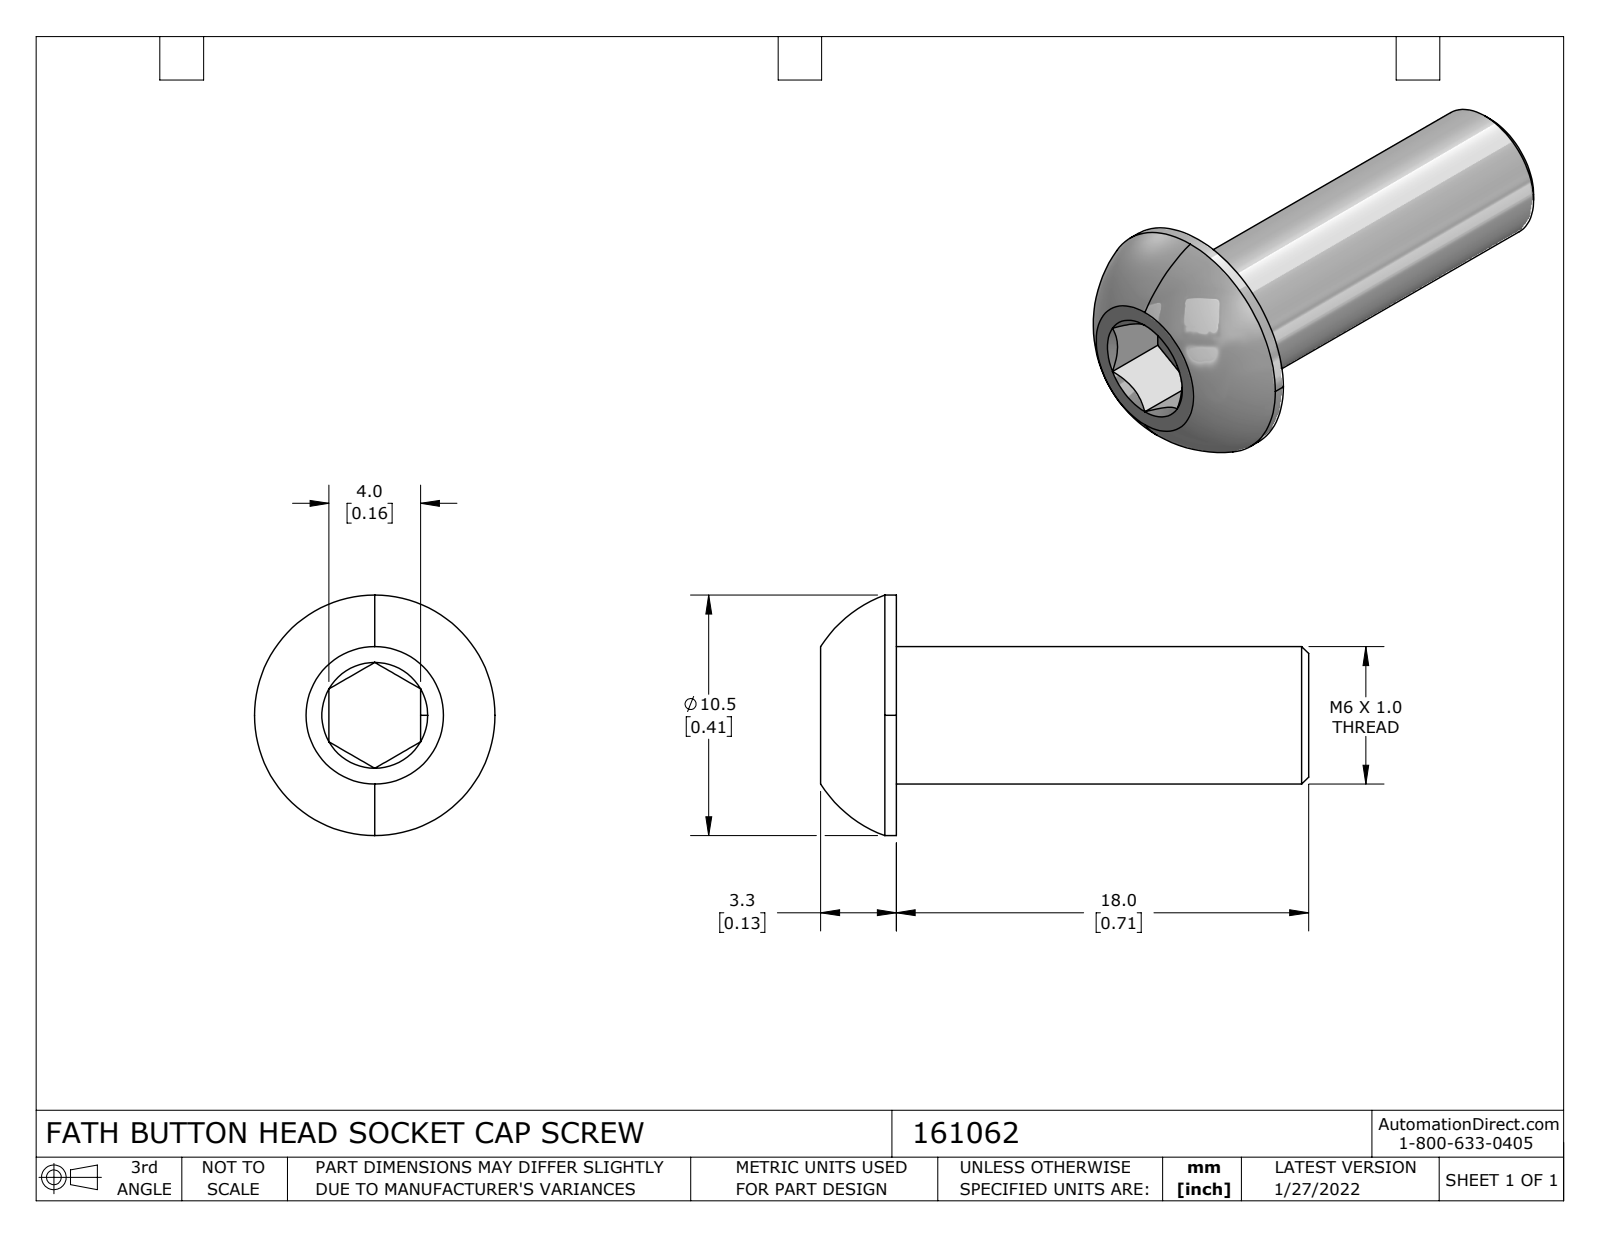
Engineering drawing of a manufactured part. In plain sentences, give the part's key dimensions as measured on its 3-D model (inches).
The part is named "161062". Its 3-D file was written by "SolidWorks 2021 (CONFIG_CONTROL_DESIGN)". It is 1 solid with 25 faces: 10 planar, 4 cylindrical and 11 other. Overall it measures 0.839 by 0.413 by 0.413 inches. Its volume is 0.042 cubic inches and its surface area 0.935 square inches. Round bosses or shafts: 1 of diameter 0.413, 1 of diameter 0.236. The main face-to-face distances are 0.709, 0.157, 0.728, 0.02, 0.839, 0.13, 0.11.
